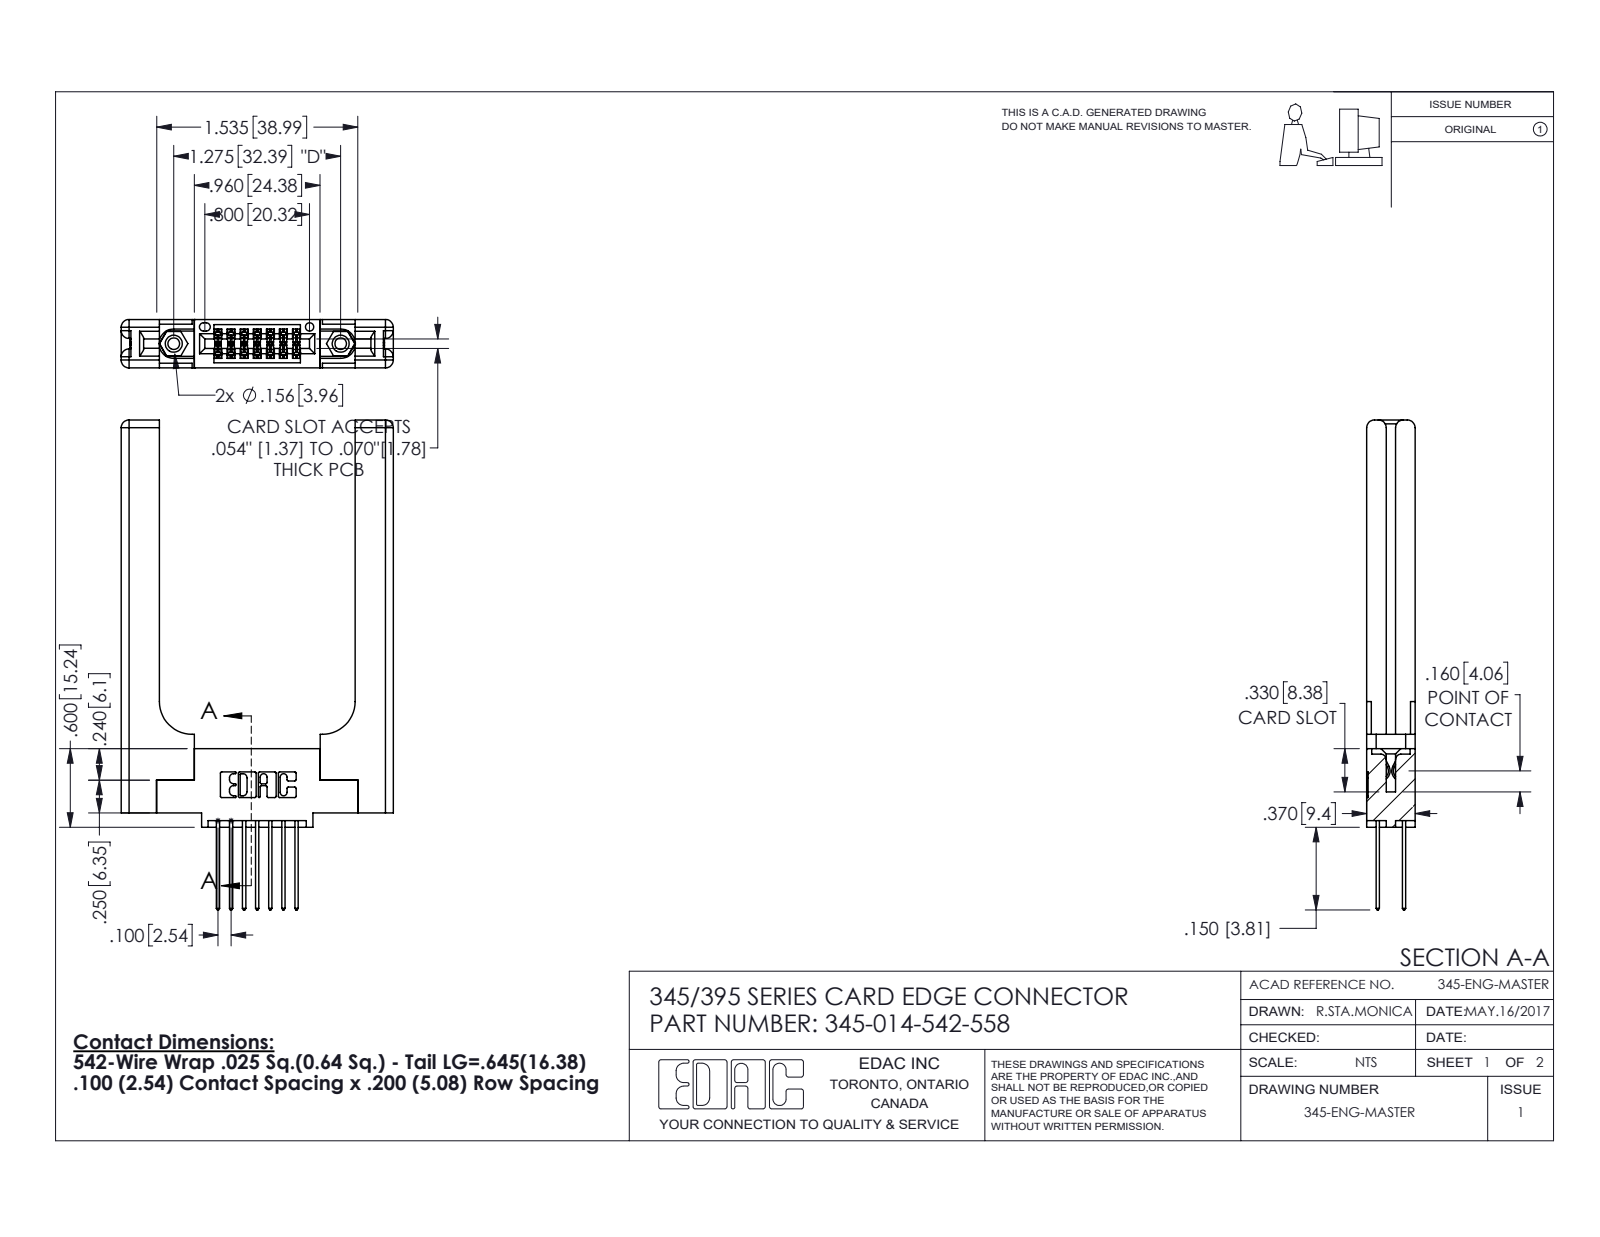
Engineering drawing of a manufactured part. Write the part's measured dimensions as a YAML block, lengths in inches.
part_name: "345 Part_0.110 Offset - 0.156 Dia-TH; 345-014-542-558; 345-220-058_345-220-058; 345-250-001_345-250-001-102 (+1 more)"
step_written_by: "SolidWorks 2016 (CONFIG_CONTROL_DESIGN)"
units: inches
bodies: {solids: 19, faces: 1086, planar: 694, cylindrical: 332, other: 60}
overall_size: [3.742, 2.079, 0.37]
volume: 0.81
surface_area: 18.4
round_holes:
  - {diameter: 0.089, count: 2}
  - {diameter: 0.125, count: 2}
  - {diameter: 0.156, count: 2}
  - {diameter: 0.064, count: 1}
round_bosses_or_shafts:
  - {diameter: 0.155, count: 2}
partial_cylinders:
  - {radius: 0.01, count: 22}
  - {radius: 0.006, count: 21}
  - {radius: 0.06, count: 16}
  - {radius: 0.01, count: 14}
  - {radius: 0.007, count: 6}
  - {radius: 0.031, count: 6}
  - {radius: 0.026, count: 3}
  - {radius: 0.014, count: 2}
face_to_face_distances: [0.37, 0.072, 0.15, 0.22, 0.148, 0.077, 0.298, 1.496, 0.225, 0.2]
hole_center_spacings: [0.27, 1.045, 1.275]
